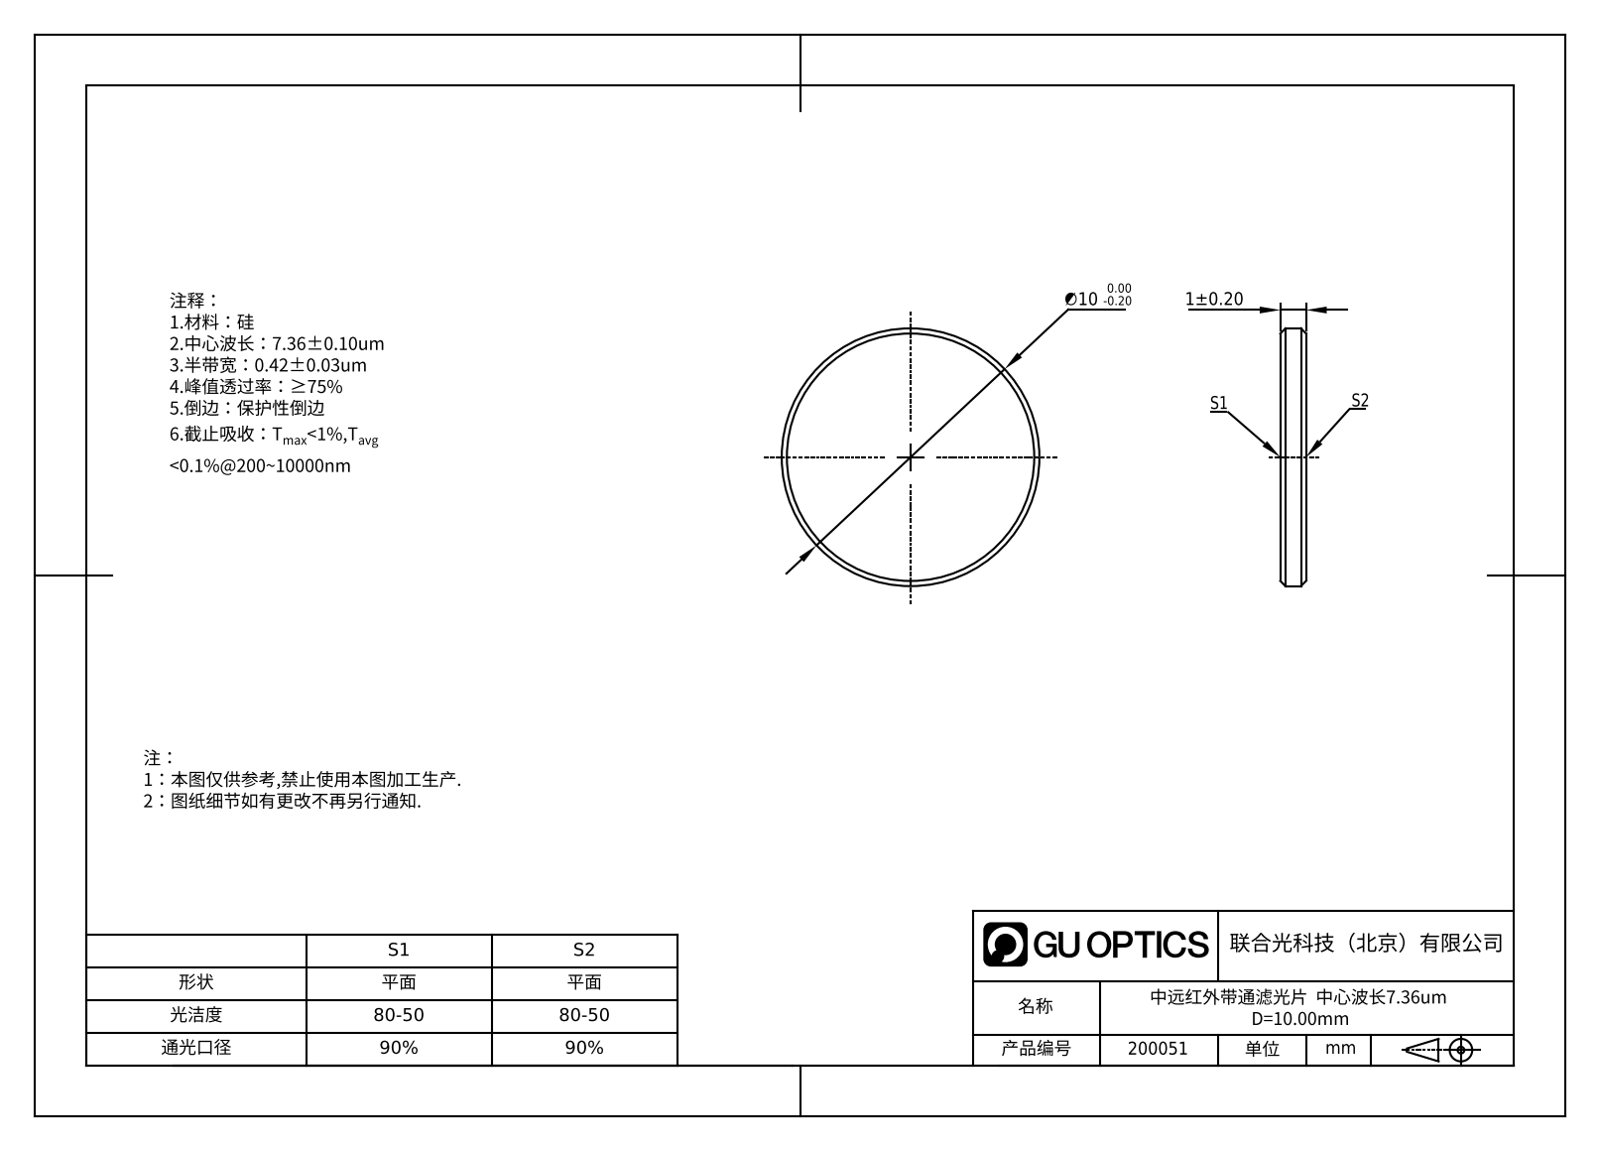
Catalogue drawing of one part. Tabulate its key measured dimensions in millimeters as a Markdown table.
| quantity | value |
| --- | --- |
| part name | GNIF-420-7360-D10 |
| STEP written by | SolidWorks 2022 (AUTOMOTIVE_DESIGN) |
| units | millimeters |
| bodies | 1 solid, 8 faces (2 planar, 2 cylindrical, 4 other) |
| overall size | 10 × 10 × 1 |
| volume | 77 mm³ |
| surface area | 181 mm² |
| round bosses / shafts (diameter × count) | 10 × 1 |
| main face-to-face distances | 1 |
